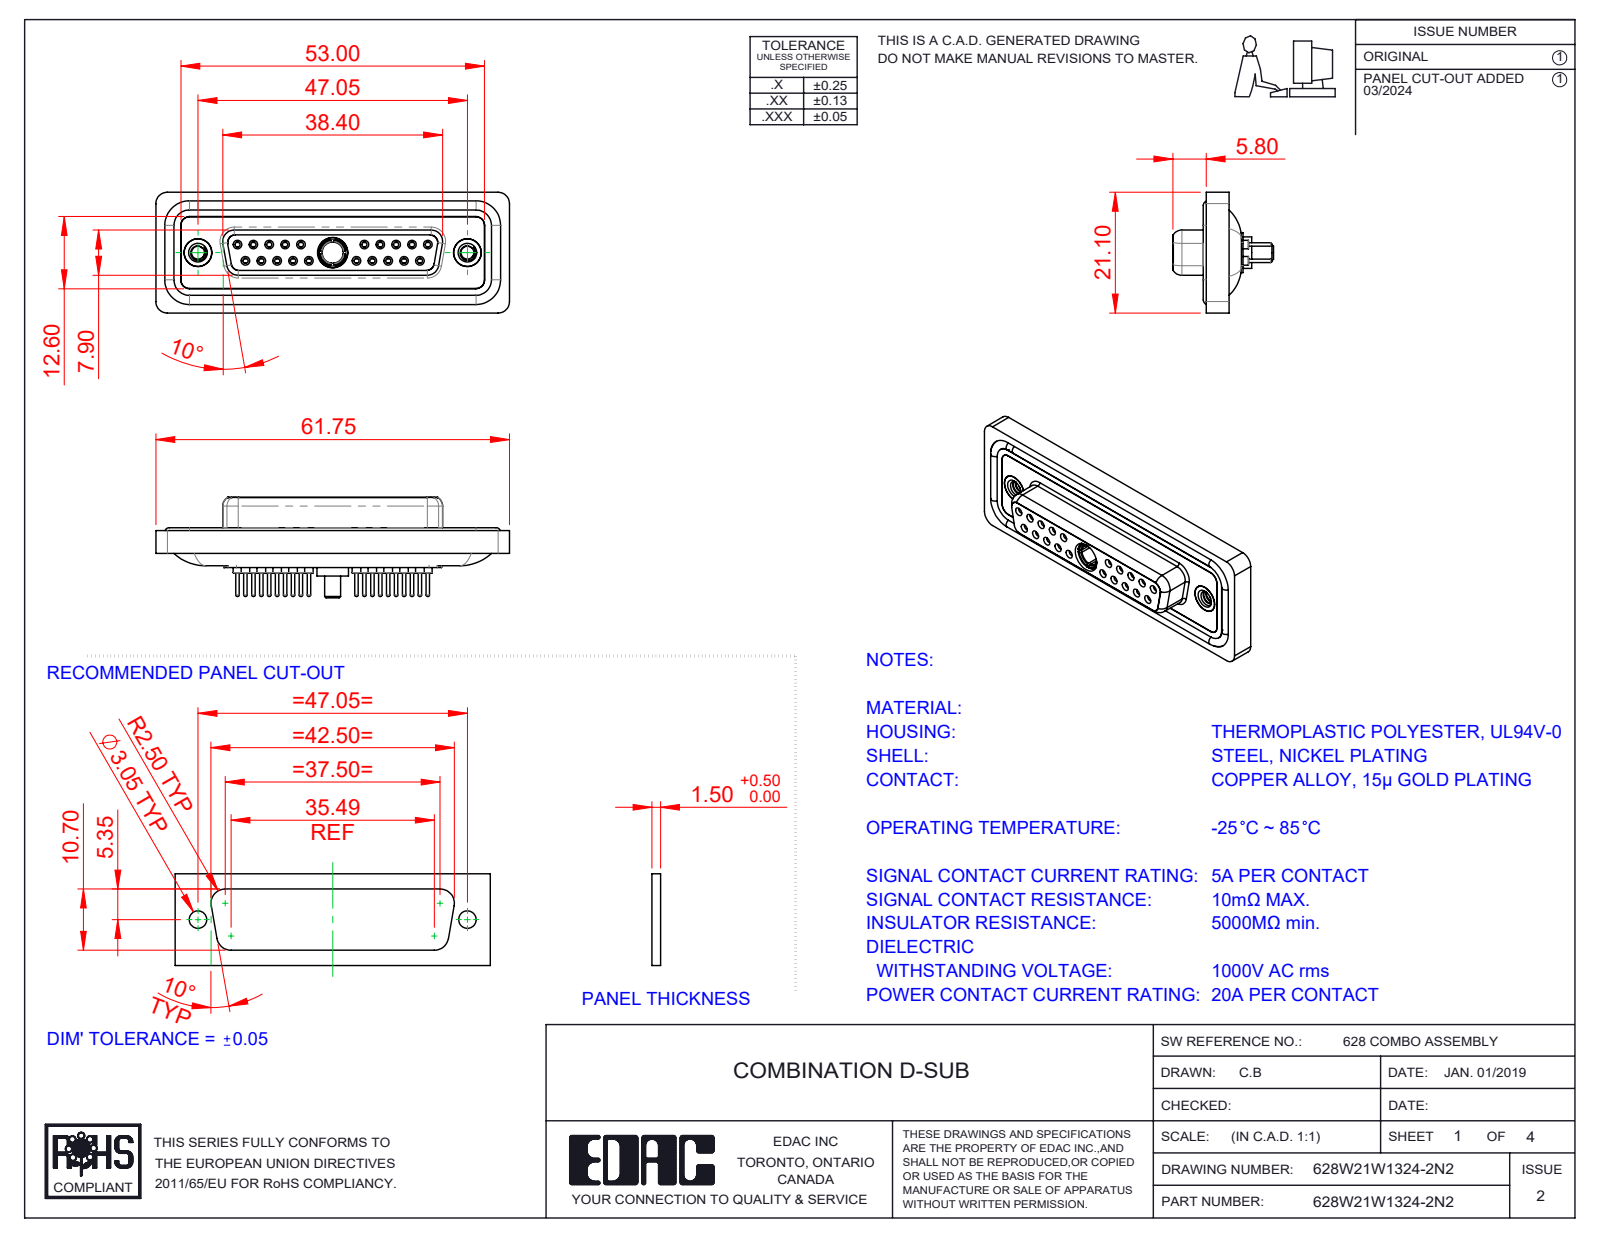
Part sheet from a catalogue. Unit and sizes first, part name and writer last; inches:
Units: inches
Overall size (bounding box): 2.431 × 0.831 × 0.691
Round holes (diameter × count): ⌀0.035 ×20, ⌀0.043 ×20, ⌀0.059 ×20, ⌀0.079 ×20, ⌀0.063 ×10, ⌀0.067 ×10, ⌀0.191 ×3, ⌀0.089 ×2, ⌀0.157 ×2, ⌀0.159 ×2, ⌀0.197 ×2, ⌀0.146 ×1
Round bosses / shafts (diameter × count): ⌀0.087 ×20, ⌀0.024 ×20, ⌀0.063 ×14, ⌀0.195 ×2, ⌀0.189 ×2, ⌀0.217 ×1, ⌀0.205 ×1, ⌀0.195 ×1
Partial cylindrical surfaces — rounded edges, fillets, slot ends (radius × count): R0.059 ×22, R0.079 ×18, R0.053 ×8, R0.063 ×8, R0.01 ×4, R0.02 ×4, R0.024 ×4, R0.026 ×4
Main face-to-face distances: 0.016, 0.071, 0.293, 0.26, 0.222, 0.02, 0.063, 0.278, 0.114, 0.043
Hole centre spacings: 0.124, 0.109, 0.218, 0.198, 0.327, 0.294, 0.654, 0.763
Volume: 0.511 in³ · Surface area: 21.7 in²
Bodies: 29 solids, 1560 faces (434 planar, 591 cylindrical, 535 other)
Part name (STEP PRODUCT): 628Combo Shell Front_25 Contacts; 628Combo Contact Row 1_24; 628Combo Housing_21W1; 628Combo Waterproof Housing_25 Contacts (+5 more)
STEP written by: SolidWorks 2023 (CONFIG_CONTROL_DESIGN)
